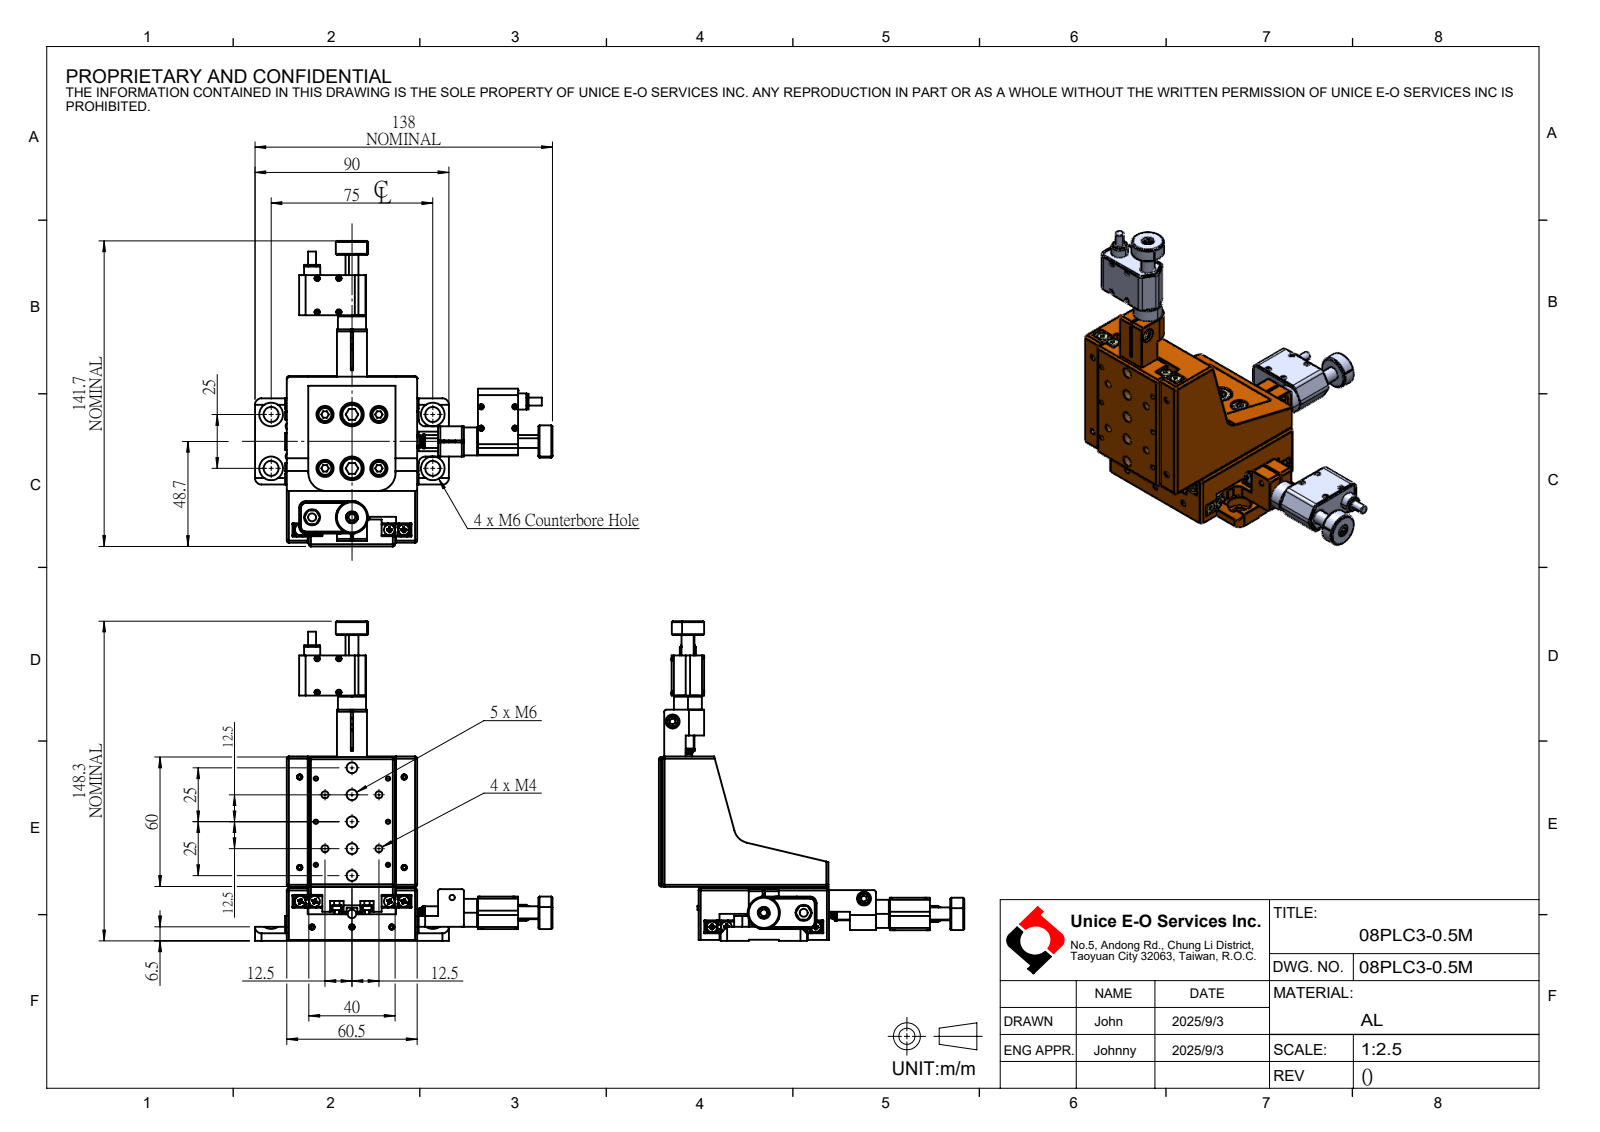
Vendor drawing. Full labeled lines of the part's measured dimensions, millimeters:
Part name (STEP PRODUCT): 08PLC3-0.5M
STEP written by: SolidWorks 2024 (CONFIG_CONTROL_DESIGN)
Units: millimetres
Bodies: 0 solids, 1547 faces (897 planar, 383 cylindrical, 267 other)
Overall size (bounding box): 148.27 × 141.72 × 138.02
Round holes (diameter × count): ⌀2.5 ×18, ⌀2.05 ×12, ⌀8 ×6, ⌀11 ×6, ⌀5 ×5, ⌀2 ×4, ⌀3.3 ×4, ⌀7 ×4, ⌀5.6 ×3, ⌀6.5 ×3, ⌀7.5 ×3, ⌀9.5 ×3
Round bosses / shafts (diameter × count): ⌀5 ×12, ⌀2 ×9, ⌀4 ×7, ⌀15 ×3, ⌀7 ×3, ⌀6.4 ×3, ⌀6 ×3, ⌀3.7 ×3
Partial cylindrical surfaces — rounded edges, fillets, slot ends (radius × count): R1 ×41, R3 ×12, R2 ×10, R2.5 ×3, R1.5 ×2, R7 ×2, R8.5 ×2, R0.7 ×1
Main face-to-face distances: 3, 6, 9, 60.5, 12.5, 16.5, 12, 11.8, 11.5, 6.75
Hole centre spacings: 25, 12.5, 8.62, 13.2, 17.68, 20, 27.95, 30.2
